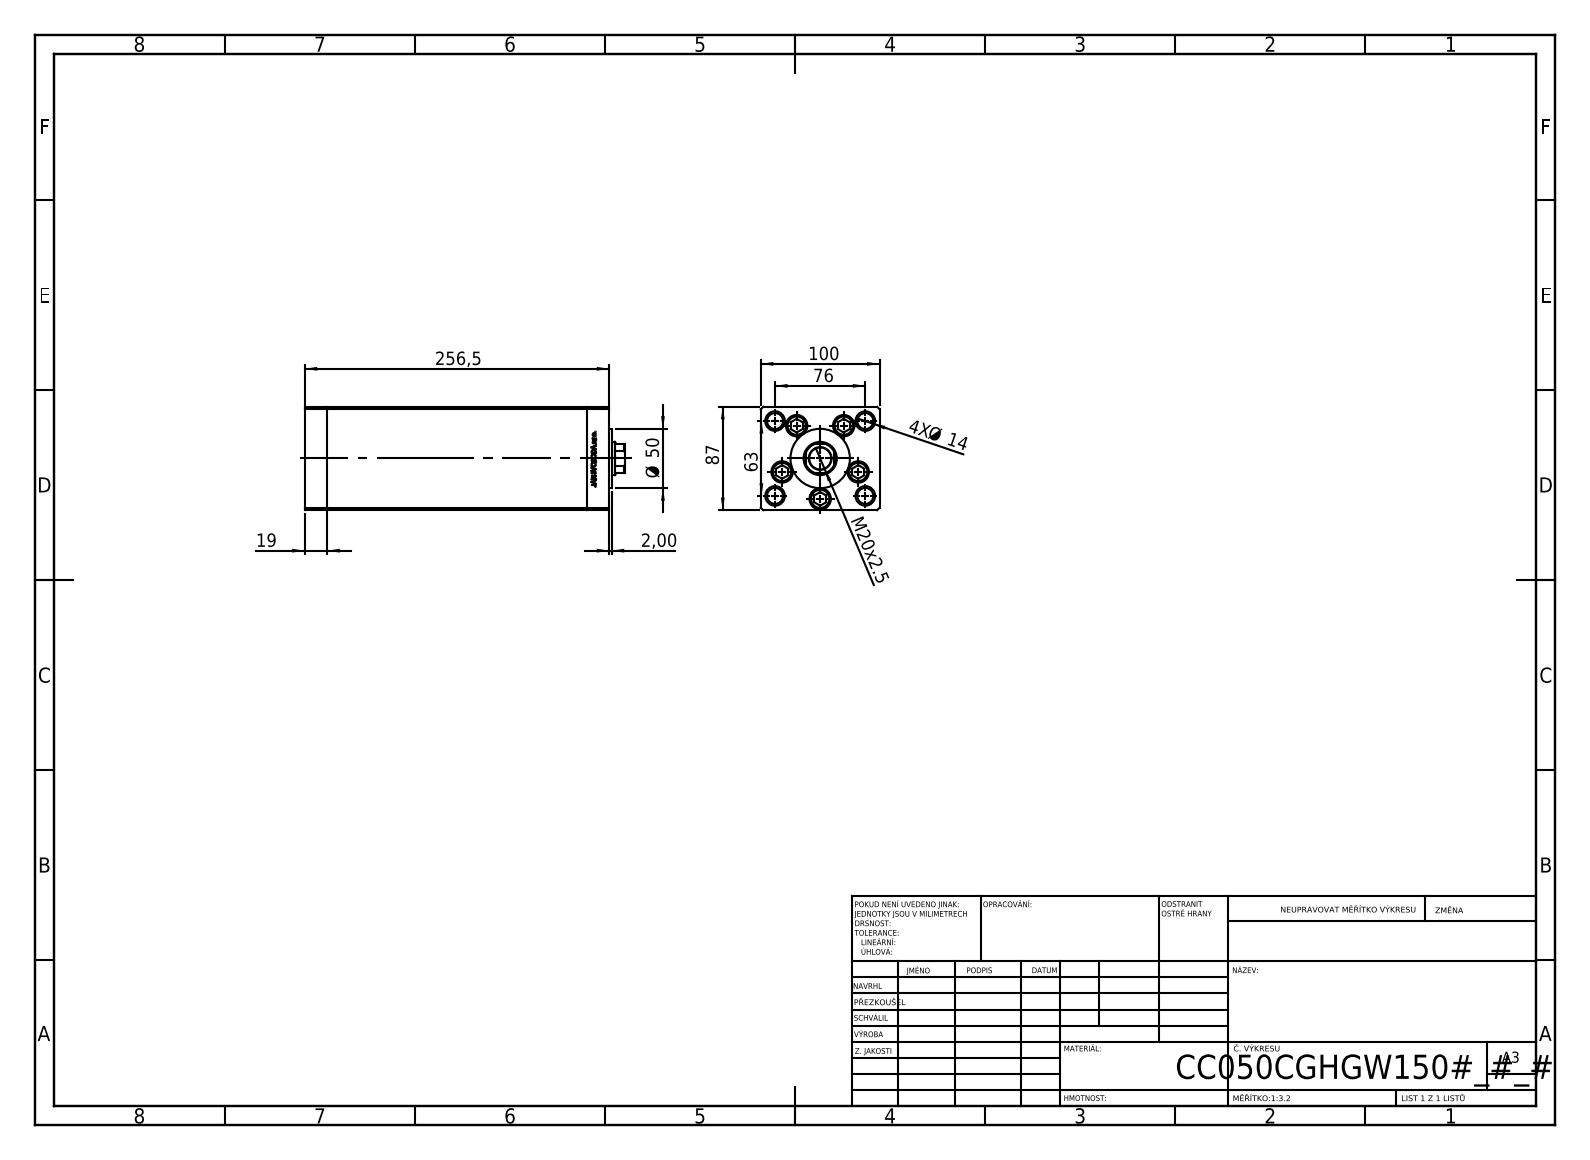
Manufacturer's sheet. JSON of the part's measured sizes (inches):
{"part_name": "V220C FRONT; V220C_C MIDDLE; V220C_VC_C; V220C BACK_C (+1 more)", "step_written_by": "SolidWorks 2019 (CONFIG_CONTROL_DESIGN)", "units": "inches", "bodies": {"solids": 13, "faces": 1186, "planar": 548, "cylindrical": 176, "other": 462}, "overall_size": [10.61, 3.937, 3.425], "volume_in3": 111.1, "surface_area_in2": 433.2, "round_holes": [[0.531, 9], [0.709, 5], [0.079, 4], [0.472, 4], [0.518, 4], [0.65, 4], [0.669, 1], [0.728, 1], [1.102, 1]], "round_bosses_or_shafts": [[0.315, 5], [0.669, 4], [1.969, 1]], "partial_cylinders_radius": [[0.037, 2], [0.531, 1]], "face_to_face_distances": [3.937, 3.425, 0.748, 8.602, 9.35, 1.348, 10.098, 8.75, 8.002, 0.6], "hole_center_spacings": [1.339, 1.943, 0.732, 0.828, 1.499, 1.546, 1.607, 1.702]}
